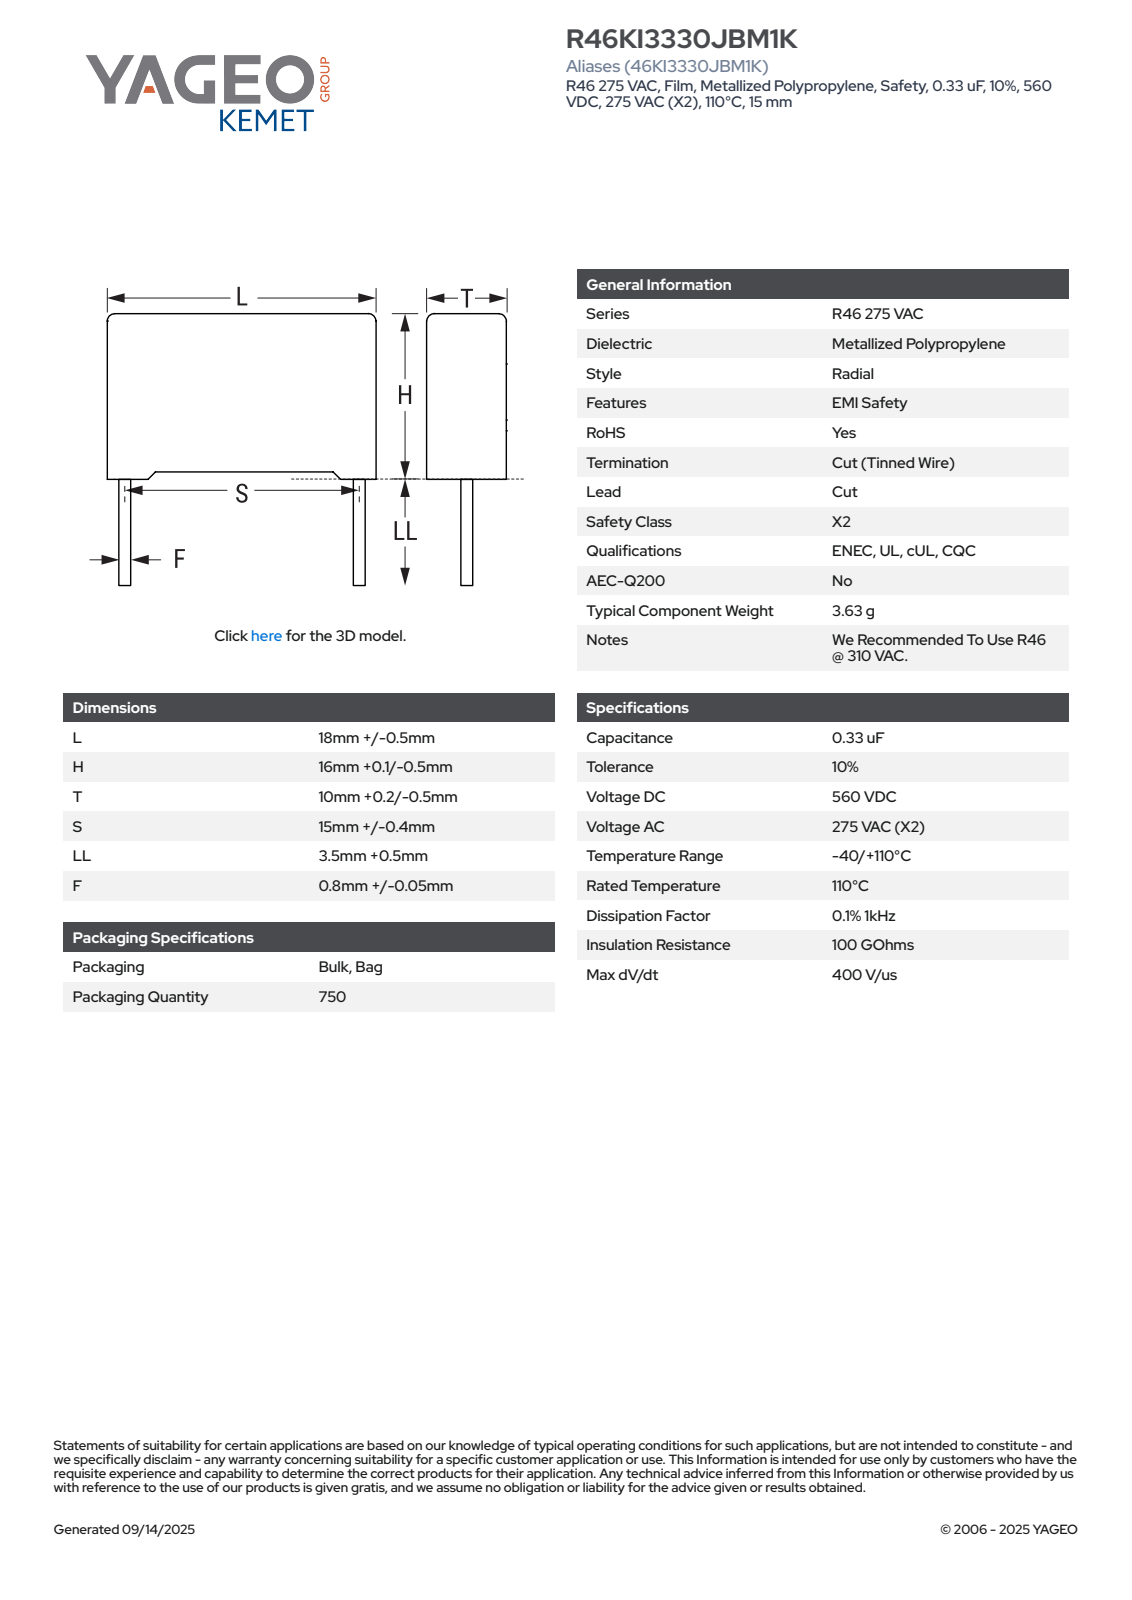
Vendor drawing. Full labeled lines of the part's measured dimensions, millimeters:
Part name (STEP PRODUCT): CFR_RB2_18X16X10_L18.5H16.1T10.2S15LL4F0.85
STEP written by: SolidWorks 2021 (AUTOMOTIVE_DESIGN)
Units: millimetres
Bodies: 4 solids, 85 faces (77 planar, 8 cylindrical, 0 other)
Overall size (bounding box): 20.1 × 18.5 × 10.21
Volume: 2 917 mm³ · Surface area: 1 355 mm²
Round bosses / shafts (diameter × count): ⌀0.85 ×2
Partial cylindrical surfaces — rounded edges, fillets, slot ends (radius × count): R0.5 ×4
Main face-to-face distances: 10.2, 18.5, 15.35, 0.62, 0.75, 16.1, 0.56, 15.54, 17.88, 9.58
